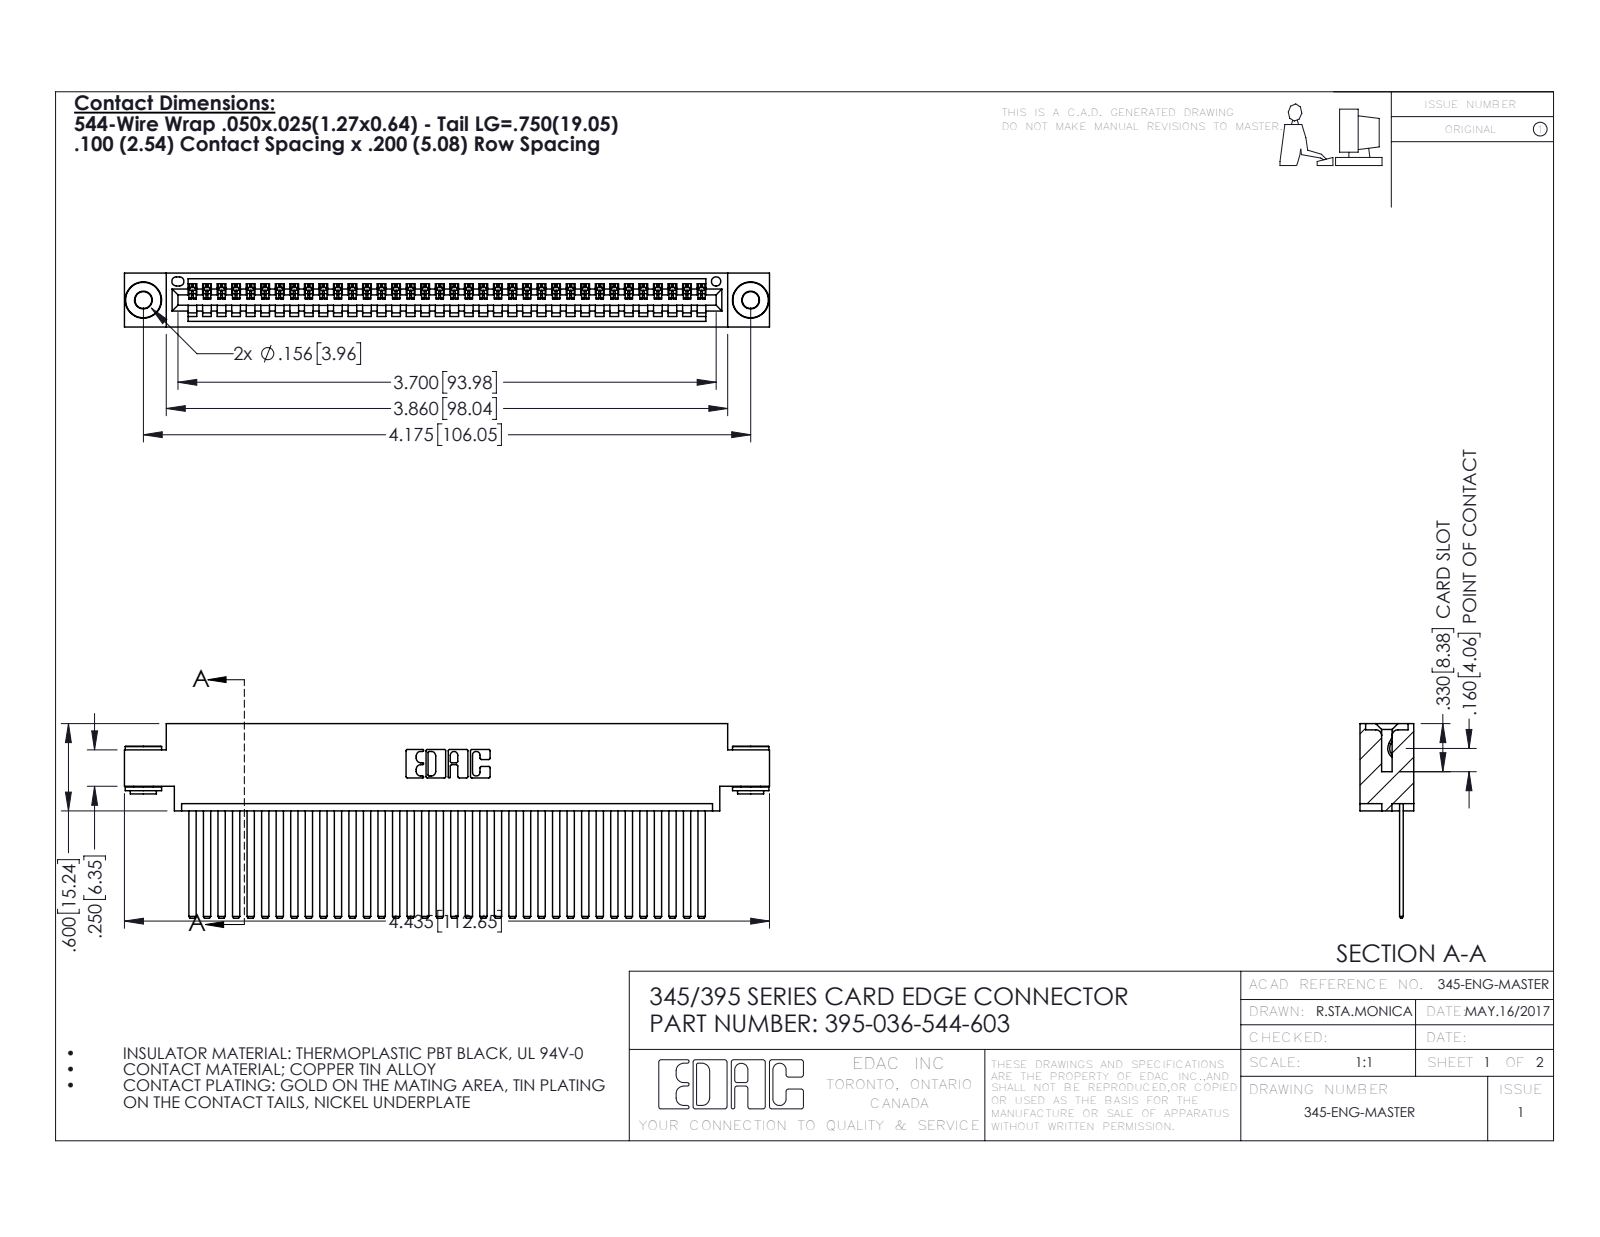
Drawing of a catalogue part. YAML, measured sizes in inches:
part_name: "345-292-001_345-293-144; 345-250-002_345-250-002-102; 345 Part_0.170 Offset - 0.156 Dia-TH; 395-036-544-603"
step_written_by: "SolidWorks 2016 (CONFIG_CONTROL_DESIGN)"
units: inches
bodies: {solids: 39, faces: 2040, planar: 1390, cylindrical: 642, other: 8}
overall_size: [4.435, 1.337, 0.37]
volume: 0.67
surface_area: 24.95
round_holes:
  - {diameter: 0.116, count: 2}
  - {diameter: 0.156, count: 2}
  - {diameter: 0.064, count: 1}
round_bosses_or_shafts:
  - {diameter: 0.25, count: 2}
  - {diameter: 0.18, count: 2}
  - {diameter: 0.136, count: 2}
partial_cylinders:
  - {radius: 0.006, count: 72}
  - {radius: 0.01, count: 22}
  - {radius: 0.007, count: 6}
  - {radius: 0.031, count: 6}
  - {radius: 0.026, count: 3}
  - {radius: 0.031, count: 2}
  - {radius: 0.04, count: 2}
  - {radius: 0.014, count: 1}
face_to_face_distances: [0.072, 0.298, 0.025, 0.098, 0.272, 0.37, 0.2, 0.225, 0.175, 0.149]
hole_center_spacings: [0.27, 3.939, 4.175]
